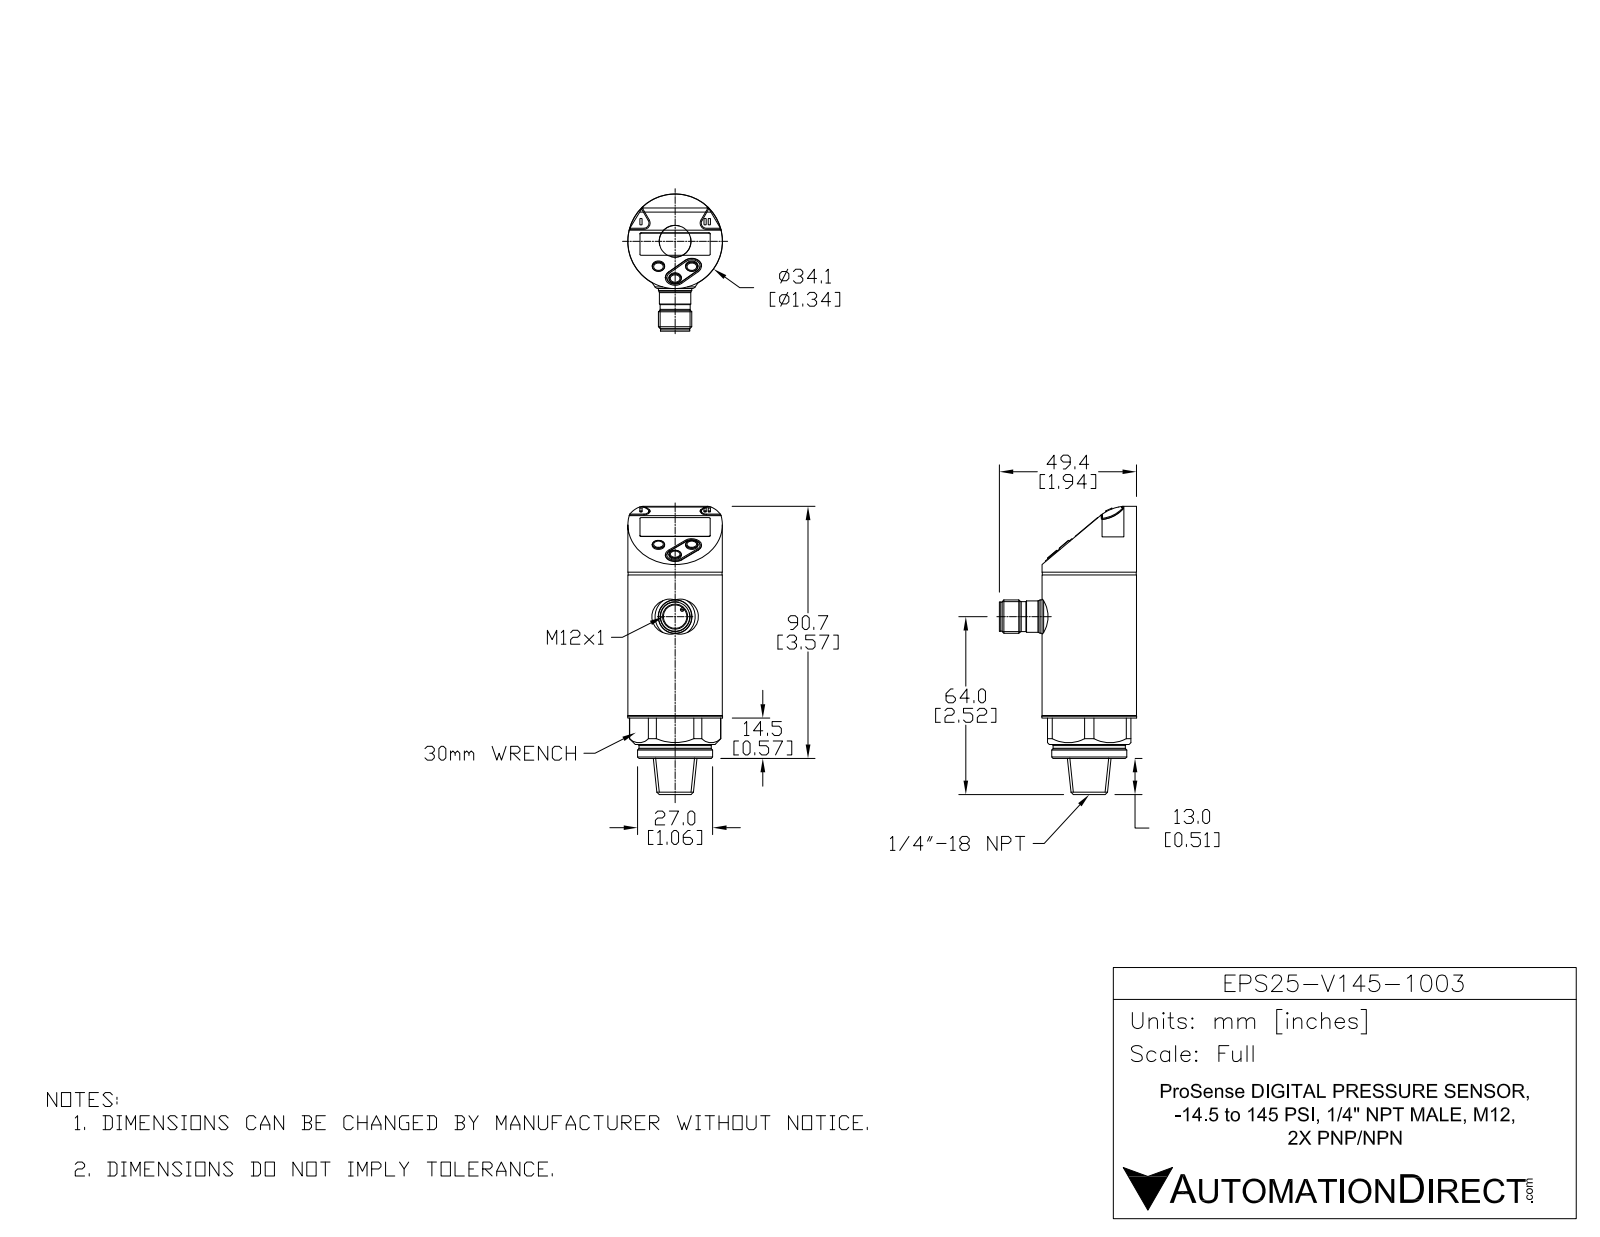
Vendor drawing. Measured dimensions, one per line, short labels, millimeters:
name: EPS25-V145-1003
written by: SolidWorks 2016 (AUTOMOTIVE_DESIGN)
unit: mm
bodies: 11 solids, 370 faces (207 planar, 84 cylindrical, 79 other)
size: 103.7 × 49.4 × 34.1
volume: 72 203 mm³; area: 21 365 mm²
holes: 1× ⌀4.2, 1× ⌀8.45
bosses: 4× ⌀1.4, 4× ⌀1, 1× ⌀34.1, 1× ⌀34, 1× ⌀33.8, 1× ⌀27, 1× ⌀26, 1× ⌀12
rounds: 2× R1.8, 2× R2.2, 2× R3, 2× R3.5, 2× R15, 1× R0.61, 1× R6.8, 1× R16.44
face distances: 0.68, 11.5, 12.18, 10.68, 1.5, 10, 2, 2.5, 14, 4
